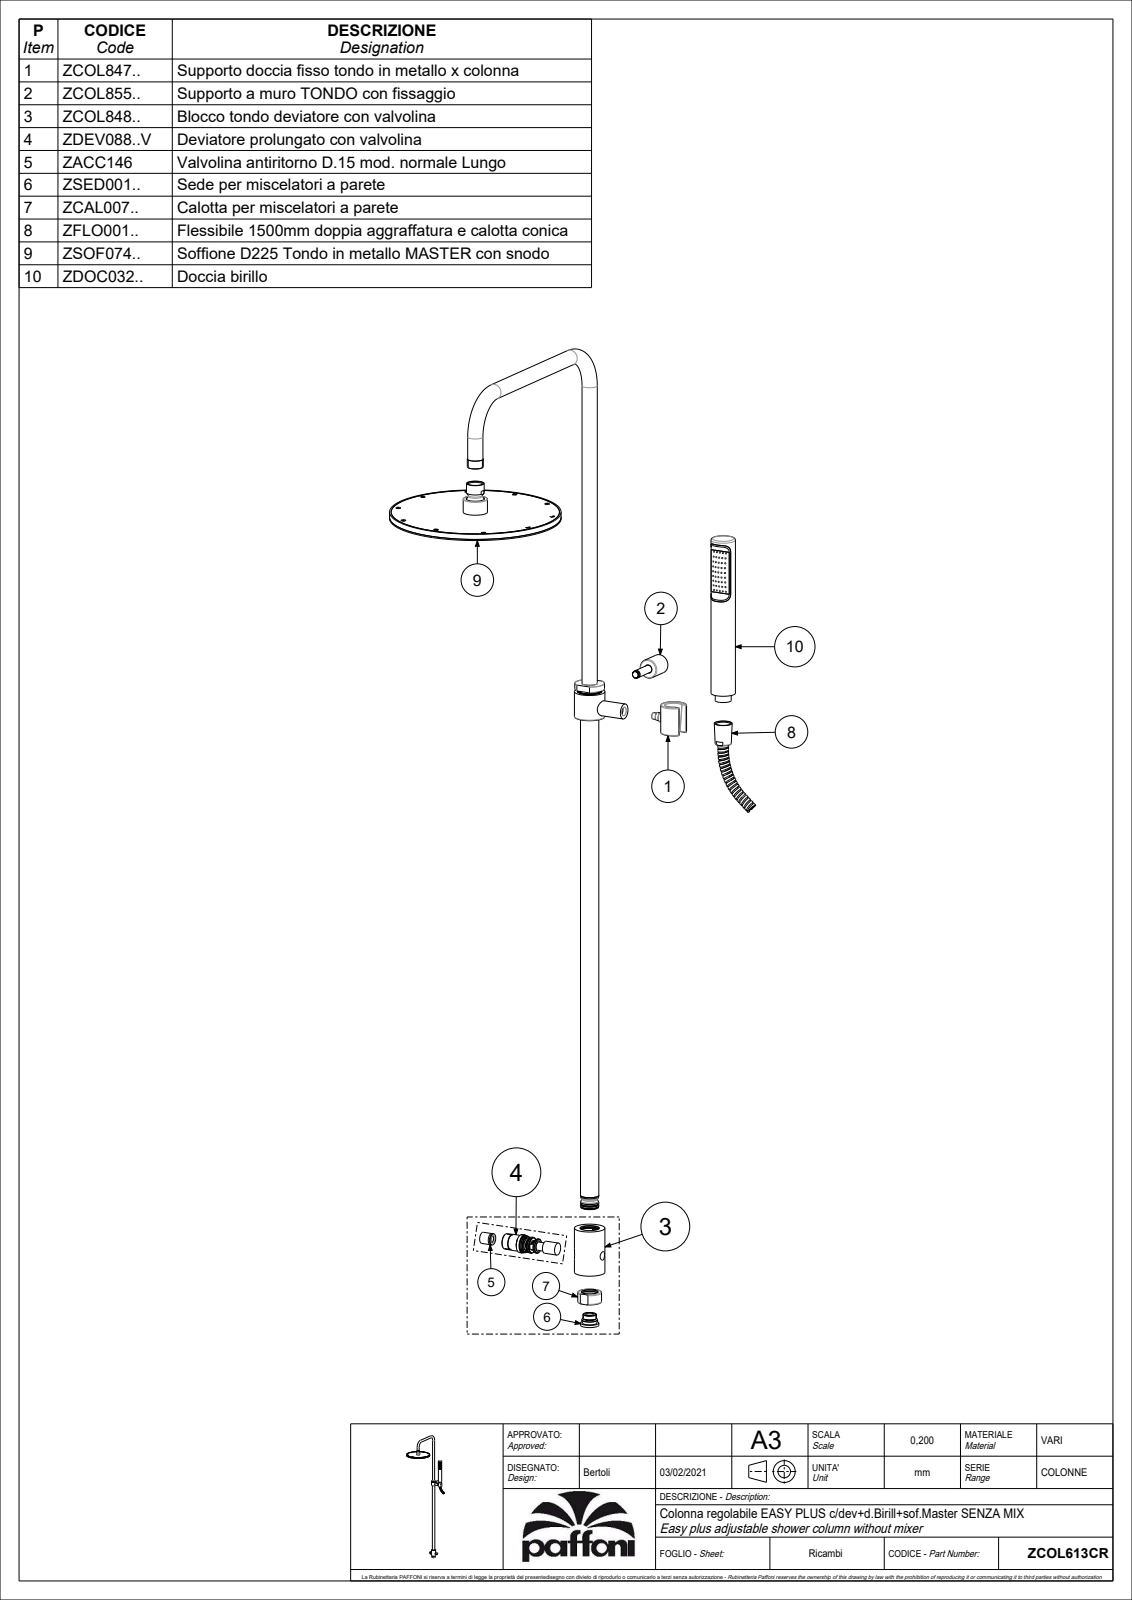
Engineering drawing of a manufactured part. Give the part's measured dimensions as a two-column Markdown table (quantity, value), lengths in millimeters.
| quantity | value |
| --- | --- |
| part name | ZCOL613CR |
| STEP written by | CREO PARAMETRIC BY PTC INC, 2020044 (CONFIG_CONTROL_DESIGN) |
| units | millimeters |
| bodies | 9 solids, 1206 faces (348 planar, 464 cylindrical, 394 other) |
| overall size | 1235 × 491.1 × 232.9 |
| volume | 637 809 mm³ |
| surface area | 404 356 mm² |
| round holes (diameter × count) | 1.2 × 80, 1.5 × 45, 5 × 4, 17 × 3, 3.3 × 2, 3.5 × 2, 4.2 × 2, 8.5 × 2, 10.5 × 2, 25 × 2, 4.5 × 1, 6.5 × 1 |
| round bosses / shafts (diameter × count) | 21 × 3, 20 × 3, 225 × 1, 40 × 1, 37 × 1, 32 × 1, 29.8 × 1, 28 × 1 |
| partial cylindrical surfaces (radius × count) | 1 × 6, 7.8 × 2, 9.8 × 2, 10 × 2, 5.5 × 1, 6.5 × 1, 15.6 × 1, 16 × 1 |
| main face-to-face distances | 6.5, 10, 331, 704, 1078.5, 1085, 321, 20, 16.5, 3.5 |
| hole center spacings | 7.91, 13.76, 6.5, 20.01, 13, 26.39, 28.16, 90 |
